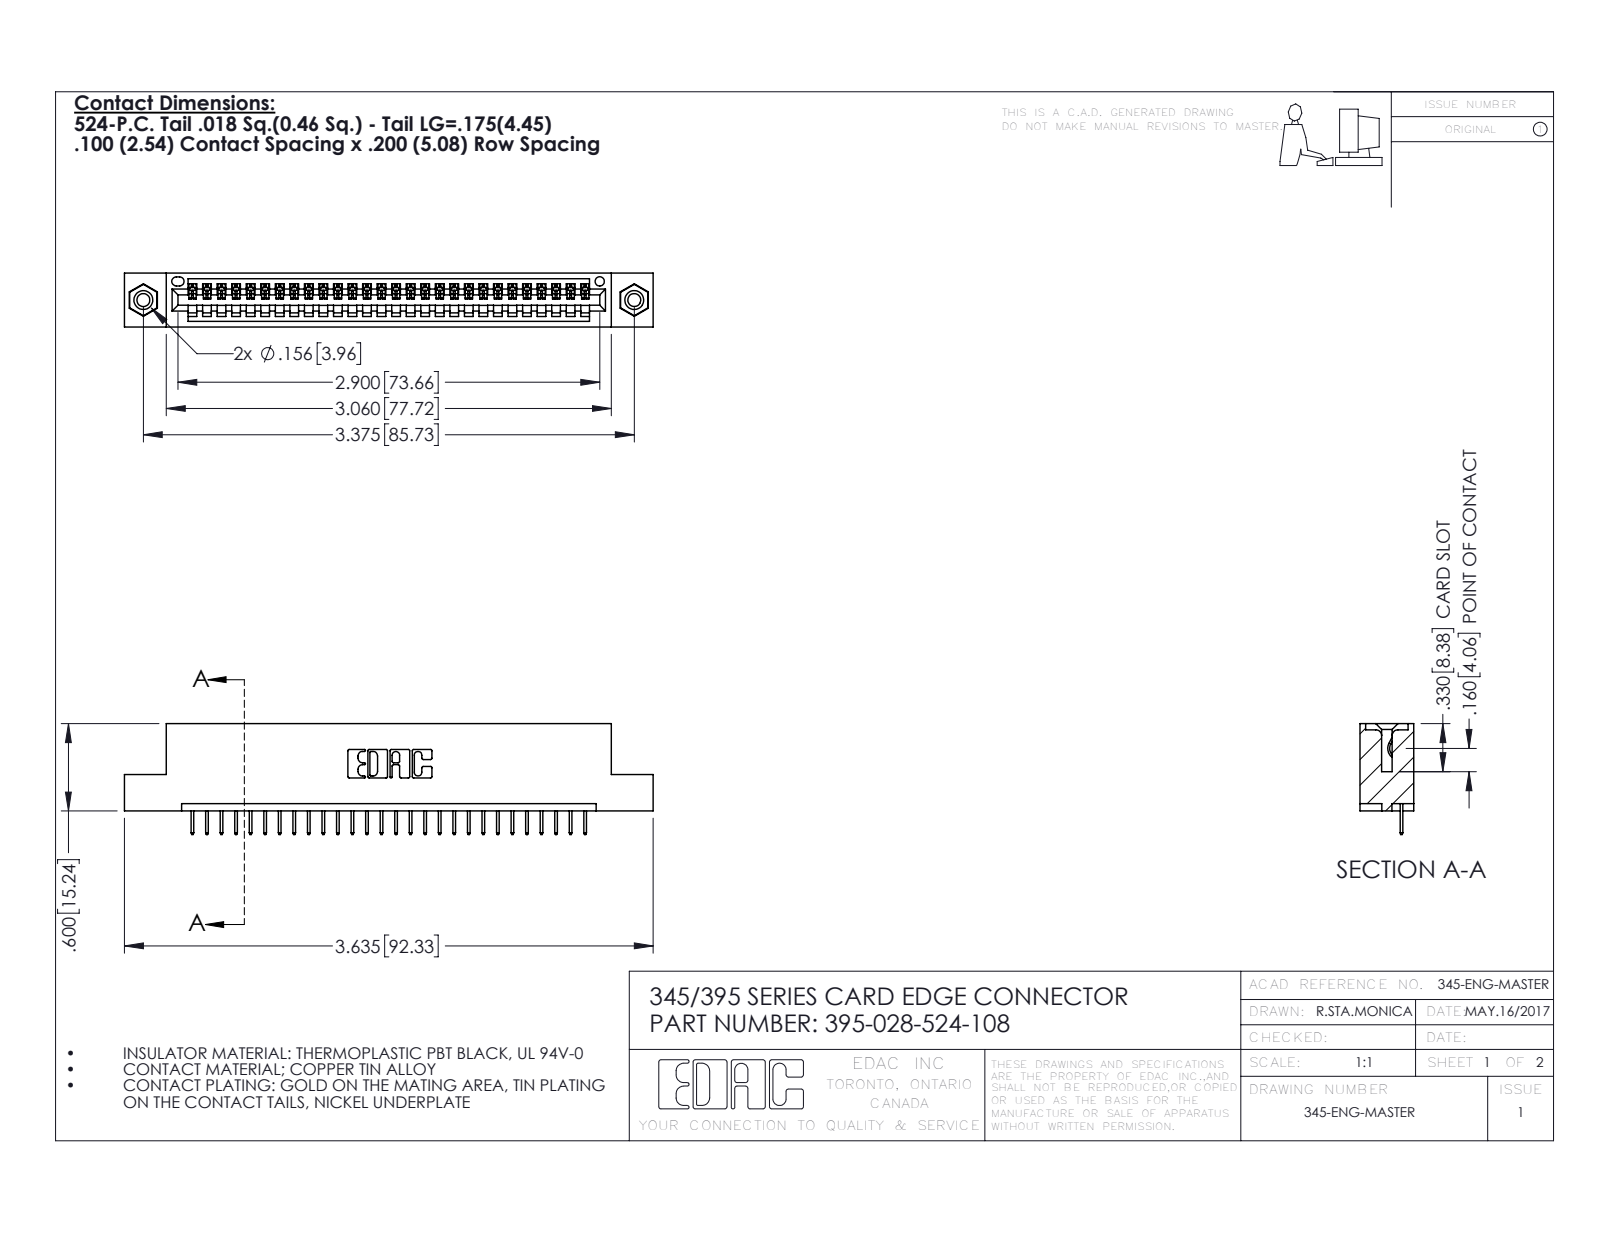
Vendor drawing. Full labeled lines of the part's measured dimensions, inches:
Part name (STEP PRODUCT): 345-250-001_345-250-003-102; 395-028-524-108; 345-292-001_345-293-124; 345 Part_Flush Mounting Lugs - 0.156 Dia-TI
STEP written by: SolidWorks 2016 (CONFIG_CONTROL_DESIGN)
Units: inches
Bodies: 31 solids, 1922 faces (1400 planar, 506 cylindrical, 16 other)
Overall size (bounding box): 3.635 × 0.762 × 0.37
Volume: 0.521 in³ · Surface area: 16.77 in²
Round holes (diameter × count): ⌀0.089 ×2, ⌀0.125 ×2, ⌀0.156 ×2, ⌀0.064 ×1
Round bosses / shafts (diameter × count): ⌀0.155 ×2
Partial cylindrical surfaces — rounded edges, fillets, slot ends (radius × count): R0.006 ×56, R0.01 ×22, R0.007 ×6, R0.031 ×6, R0.026 ×3, R0.031 ×2, R0.04 ×2, R0.014 ×1
Main face-to-face distances: 0.072, 0.298, 0.37, 0.2, 0.098, 0.272, 0.025, 0.225, 0.072, 0.149
Hole centre spacings: 0.27, 3.14, 3.375
